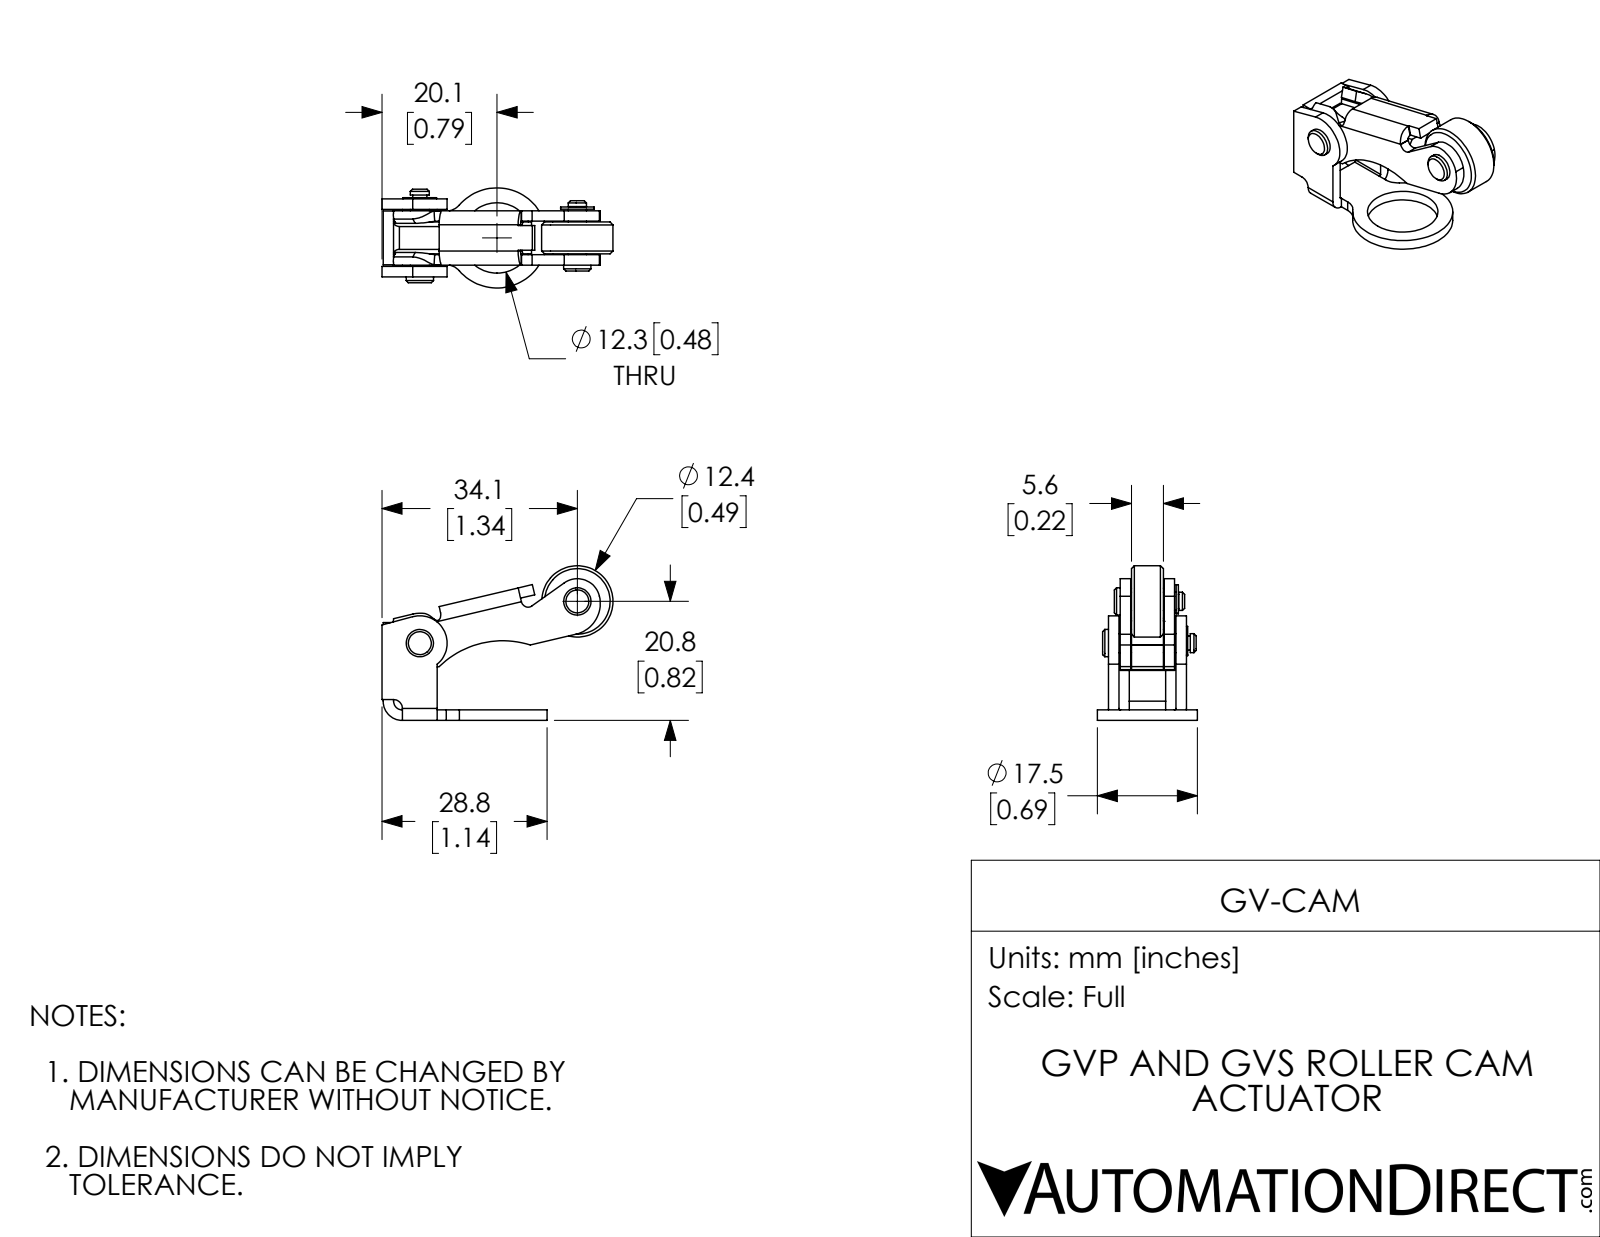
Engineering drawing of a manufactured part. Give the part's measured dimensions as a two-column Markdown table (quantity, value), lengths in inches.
| quantity | value |
| --- | --- |
| part name | GV-CAM |
| STEP written by | SolidWorks 2018 (AUTOMOTIVE_DESIGN) |
| units | inches |
| bodies | 8 solids, 213 faces (89 planar, 102 cylindrical, 22 other) |
| overall size | 1.588 × 1.063 × 0.688 |
| volume | 0.242 in³ |
| surface area | 7.735 in² |
| round holes (diameter × count) | 0.136 × 2, 0.13 × 1, 0.133 × 1, 0.484 × 1 |
| round bosses / shafts (diameter × count) | 0.187 × 2, 0.096 × 2, 0.49 × 1, 0.13 × 1, 0.125 × 1 |
| partial cylindrical surfaces (radius × count) | 0.016 × 12, 0.06 × 5, 0.047 × 3, 0.011 × 2, 0.025 × 2, 0.083 × 2, 0.088 × 2, 0.097 × 2 |
| main face-to-face distances | 0.072, 0.081, 0.383, 0.302, 0.078, 0.296, 0.224, 0.464, 0.153, 0.159 |
| hole center spacings | 1.12 |
